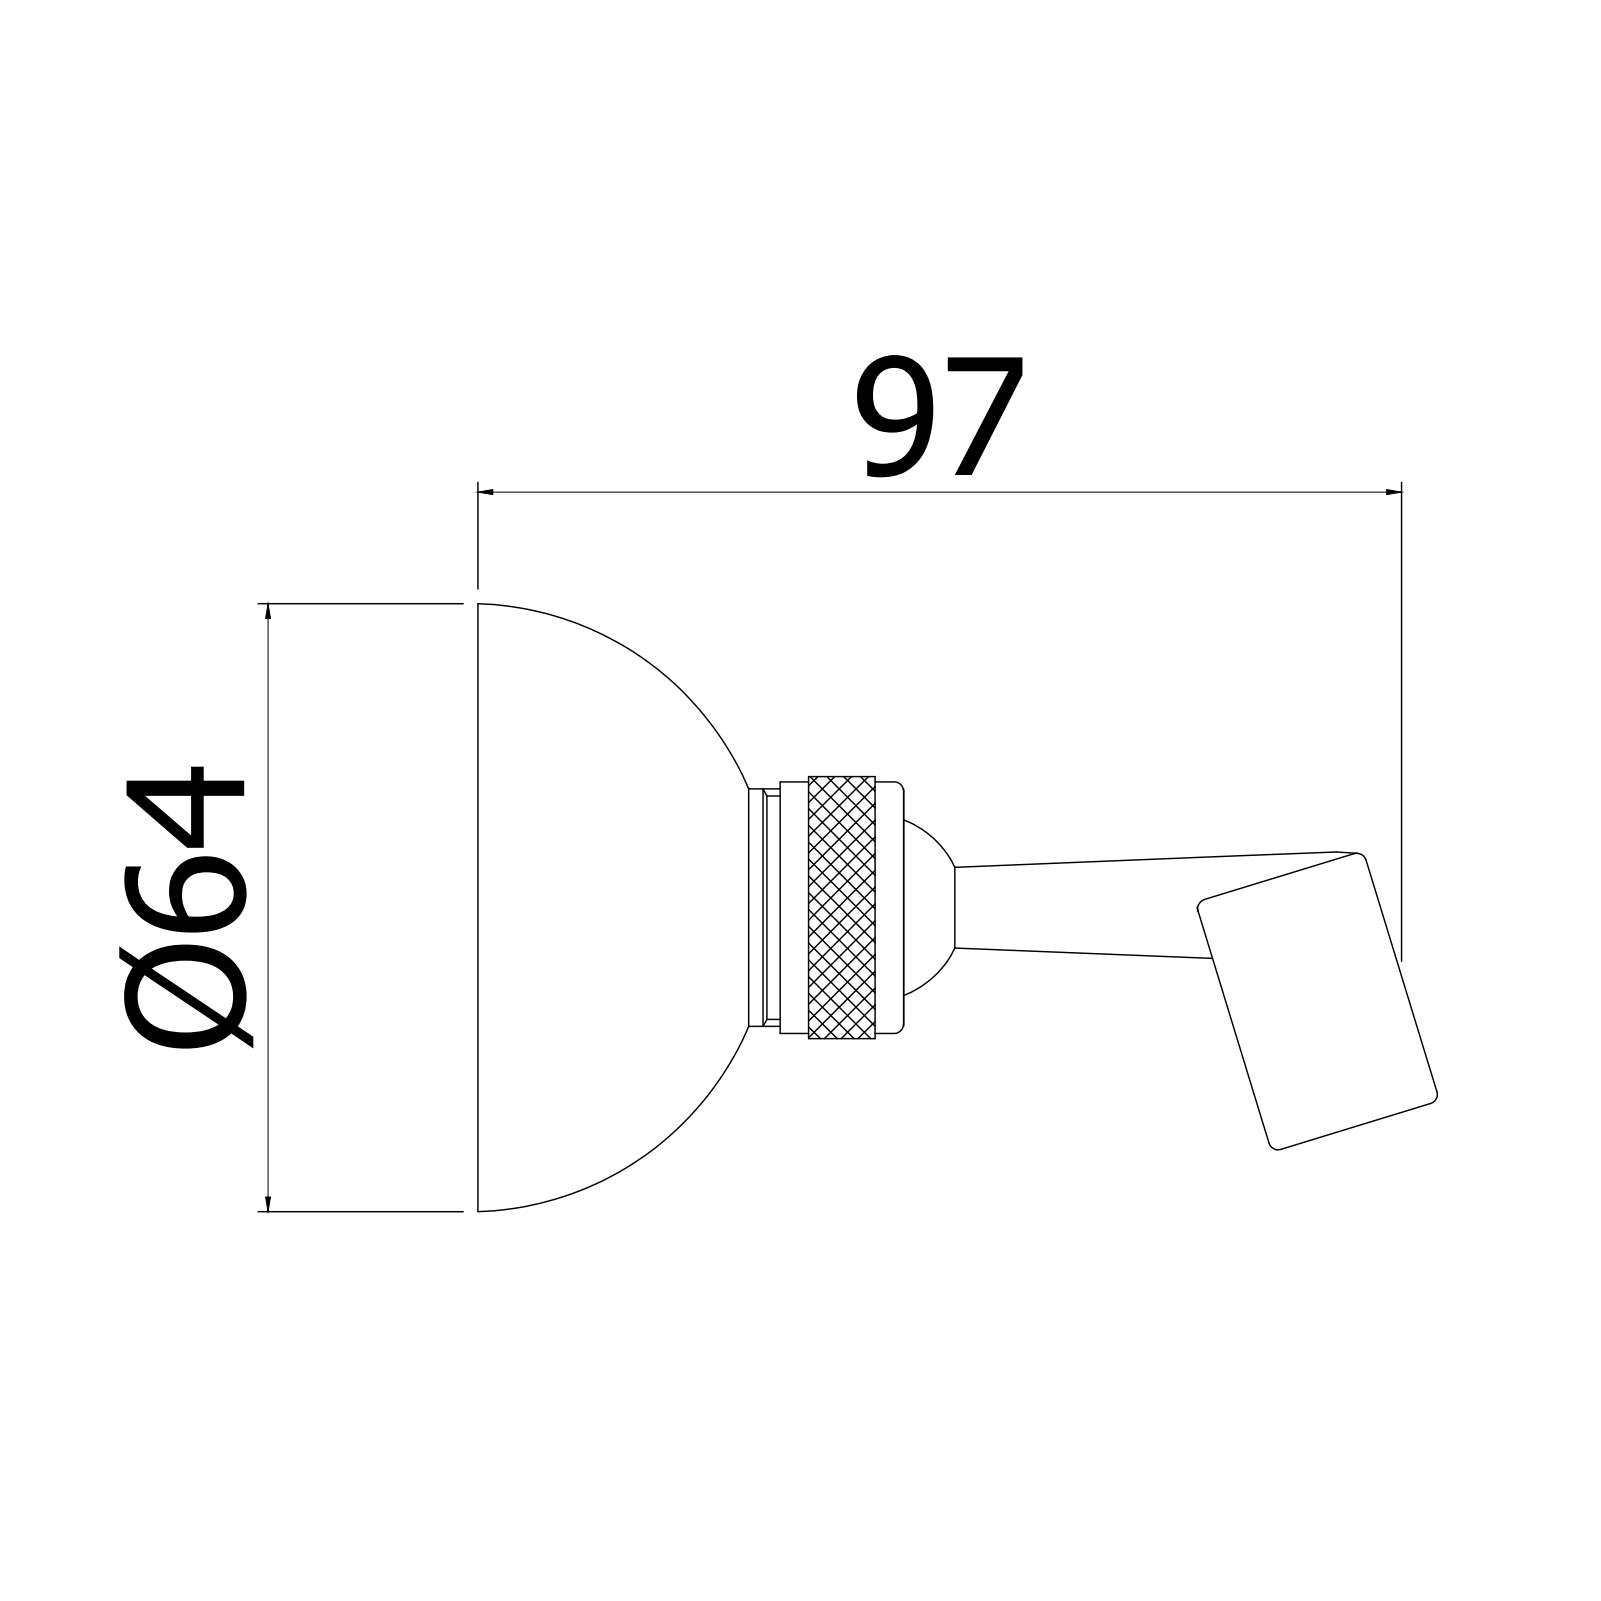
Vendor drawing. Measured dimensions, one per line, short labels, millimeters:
name: ZSUP001CR
written by: CREO PARAMETRIC BY PTC INC, 2020044 (CONFIG_CONTROL_DESIGN)
unit: mm
bodies: 1 solid, 246 faces (120 planar, 76 cylindrical, 50 other)
size: 95.47 × 68.16 × 63
volume: 21 938 mm³; area: 22 646 mm²
holes: 1× ⌀6, 1× ⌀12.5, 1× ⌀18, 1× ⌀19, 1× ⌀21, 1× ⌀23.5
bosses: 1× ⌀29, 1× ⌀27, 1× ⌀26, 1× ⌀24.5, 1× ⌀21.5, 1× ⌀20.5, 1× ⌀18.5, 1× ⌀9.5
rounds: 1× R10, 1× R12
face distances: 15.5, 15, 12.51, 4, 14, 20.42, 12.52, 11.58, 31, 19.42
